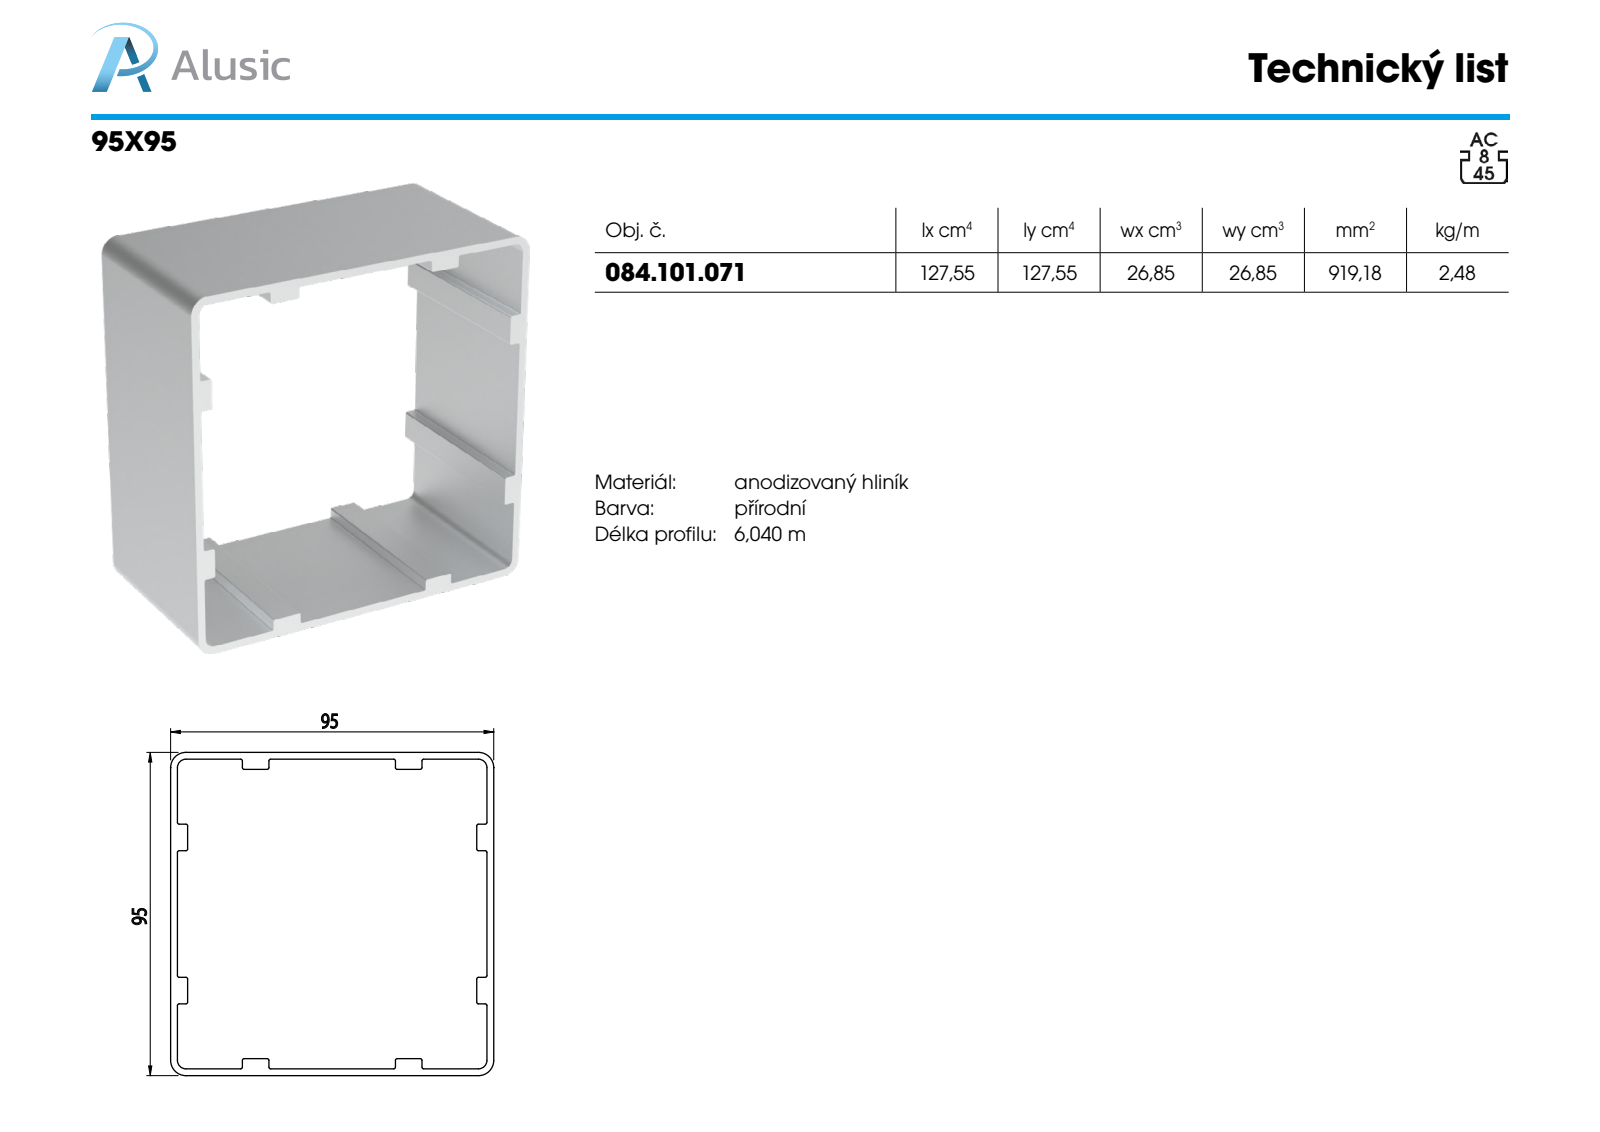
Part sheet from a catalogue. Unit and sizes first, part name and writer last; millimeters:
Units: millimetres
Overall size (bounding box): 100 × 95 × 95
Partial cylindrical surfaces — rounded edges, fillets, slot ends (radius × count): R0.5 ×32, R2.5 ×4, R4.5 ×4
Main face-to-face distances: 2, 93, 95, 91, 5, 90, 3, 88, 85, 21.1
Volume: 91 918 mm³ · Surface area: 79 150 mm²
Bodies: 1 solid, 82 faces (42 planar, 40 cylindrical, 0 other)
Part name (STEP PRODUCT): 084.101.071
STEP written by: SolidWorks 2018 (AUTOMOTIVE_DESIGN)
